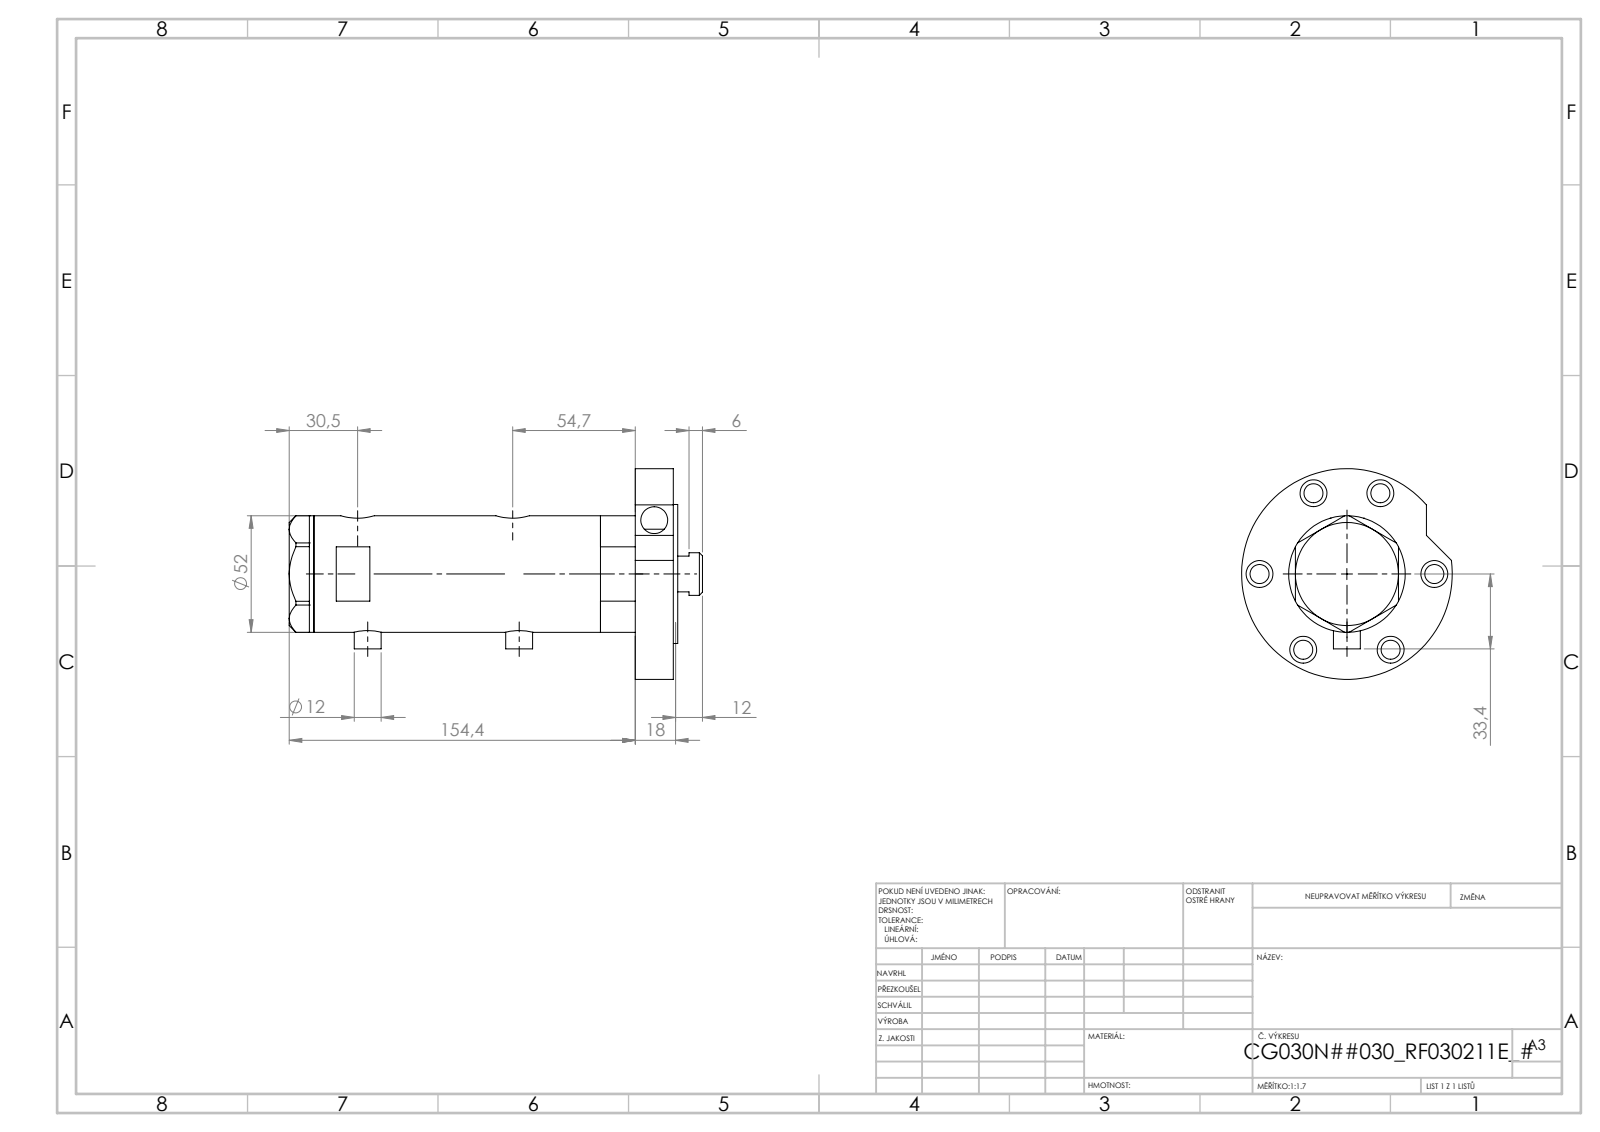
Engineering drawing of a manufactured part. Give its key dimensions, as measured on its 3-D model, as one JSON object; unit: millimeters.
{"part_name": "V270CG_BACK; V270CG_MIDDLE; V270CG_FRONT; V270CG_VC (+1 more)", "step_written_by": "SolidWorks 2019 (CONFIG_CONTROL_DESIGN)", "units": "millimeters", "bodies": {"solids": 5, "faces": 184, "planar": 78, "cylindrical": 86, "other": 20}, "overall_size": [179.02, 94, 94], "volume_mm3": 401261, "surface_area_mm2": 98484, "round_holes": [[12, 7], [8.5, 6], [5, 2], [9.73, 2], [12.5, 2], [15, 2], [6.5, 1], [20, 1], [21.5, 1], [30, 1], [33, 1], [40, 1]], "round_bosses_or_shafts": [[12, 2], [94, 1], [62, 1], [52, 1], [38, 1], [19, 1]], "face_to_face_distances": [17, 135.45, 152.45, 2, 154.45, 19, 23.81, 111.64, 128.64, 130.64], "hole_center_spacings": [39, 2.9, 4.5, 43.34, 56.75, 59.65, 61.25, 64.15]}
